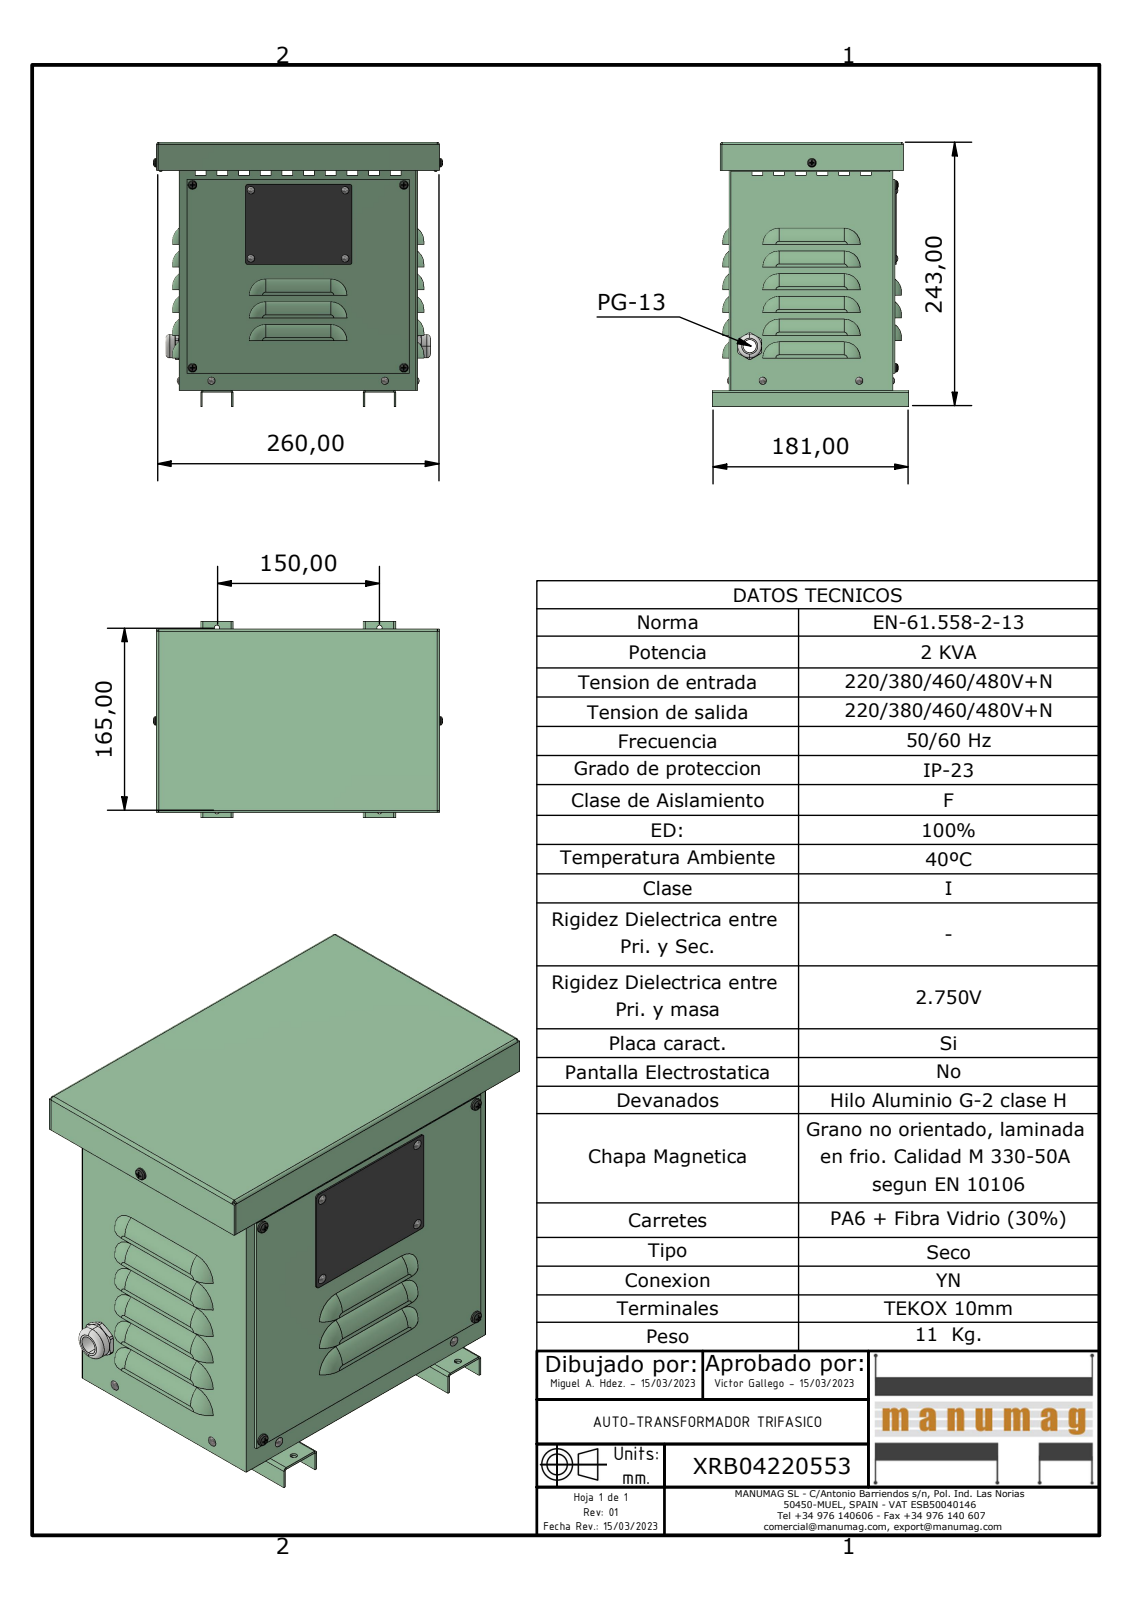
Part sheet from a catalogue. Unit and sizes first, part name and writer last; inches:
Units: inches
Overall size (bounding box): 10.517 × 9.626 × 7.126
Round holes (diameter × count): ⌀0.189 ×13, ⌀0.15 ×5, ⌀0.118 ×4, ⌀0.157 ×4, ⌀0.472 ×1, ⌀0.866 ×1
Round bosses / shafts (diameter × count): ⌀0.126 ×8, ⌀0.157 ×5, ⌀0.143 ×5, ⌀0.854 ×1, ⌀0.803 ×1, ⌀0.799 ×1, ⌀0.746 ×1
Partial cylindrical surfaces — rounded edges, fillets, slot ends (radius × count): R0.551 ×24, R0.591 ×21, R0.157 ×18, R0.059 ×13, R0.079 ×12, R0.02 ×8, R0.098 ×8, R0.571 ×6
Main face-to-face distances: 0.059, 5.886, 8.976, 8.602, 9.035, 5.965, 5.945, 0.079, 6.024, 8.543
Hole centre spacings: 6.654, 5.906, 0.835, 1.024, 1.693, 1.969, 2.135, 2.48
Volume: 36.69 in³ · Surface area: 1 038 in²
Bodies: 27 solids, 1168 faces (639 planar, 259 cylindrical, 270 other)
Part name (STEP PRODUCT): XRB04220553; JE001 - JE002 EXPORT CUERPO; JE001 - JE002 EXPORT BASE; JE001 - JE002 EXPORT PATA (+6 more)
STEP written by: Autodesk Inventor 2023 (AUTOMOTIVE_DESIGN)
